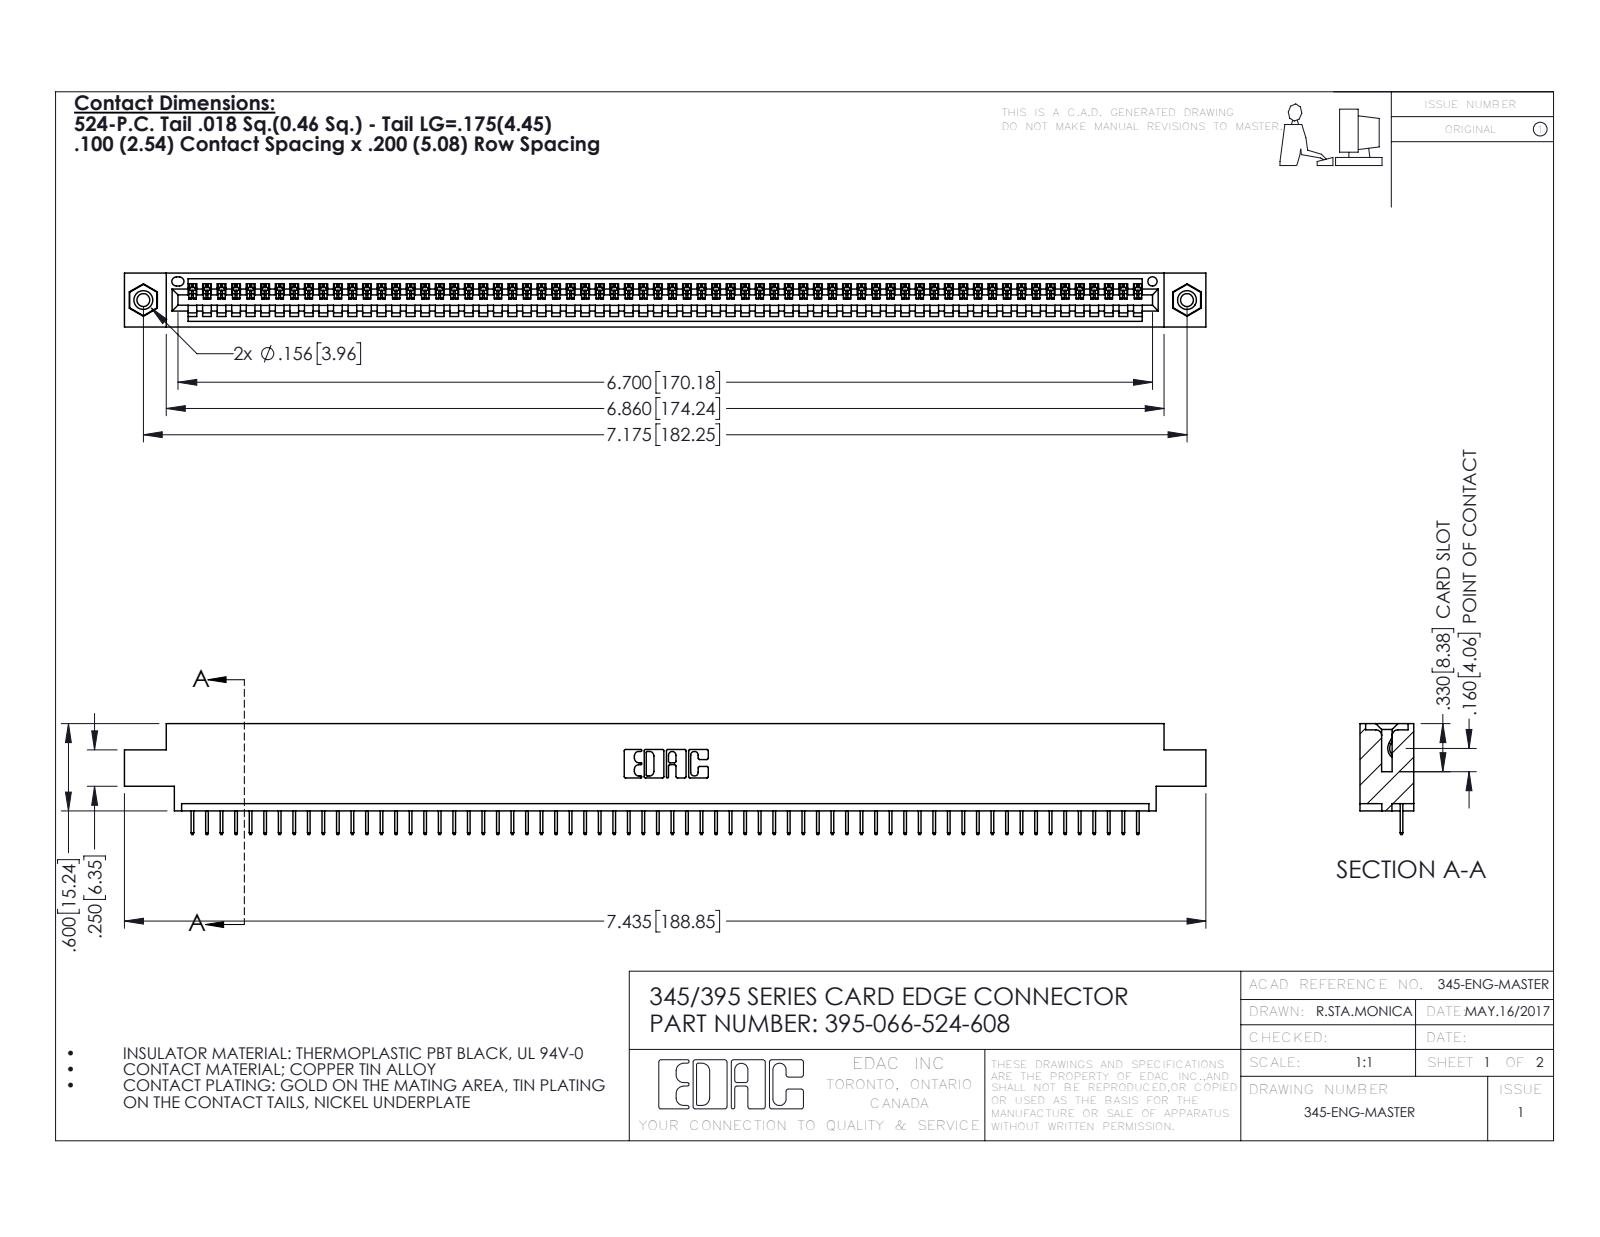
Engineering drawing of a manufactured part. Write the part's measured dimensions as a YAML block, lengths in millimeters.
part_name: "345 Part_0.170 Offset - 0.156 Dia-TI; 345-292-001_345-293-124; 395-066-524-608; 345-250-001_345-250-003-102"
step_written_by: "SolidWorks 2016 (CONFIG_CONTROL_DESIGN)"
units: millimeters
bodies: {solids: 69, faces: 4282, planar: 3152, cylindrical: 1114, other: 16}
overall_size: [188.8, 19.4, 9.4]
volume: 17750
surface_area: 23230
round_holes:
  - {diameter: 2.3, count: 2}
  - {diameter: 3.2, count: 2}
  - {diameter: 4, count: 2}
  - {diameter: 1.6, count: 1}
round_bosses_or_shafts:
  - {diameter: 3.9, count: 2}
partial_cylinders:
  - {radius: 0.2, count: 132}
  - {radius: 0.3, count: 22}
  - {radius: 0.2, count: 6}
  - {radius: 0.8, count: 6}
  - {radius: 0.7, count: 3}
  - {radius: 0.8, count: 2}
  - {radius: 1, count: 2}
  - {radius: 0.4, count: 1}
face_to_face_distances: [1.8, 7.6, 9.4, 5.1, 2.5, 6.9, 0.6, 5.7, 1.8, 4.4]
hole_center_spacings: [6.9, 176.3, 182.2]
